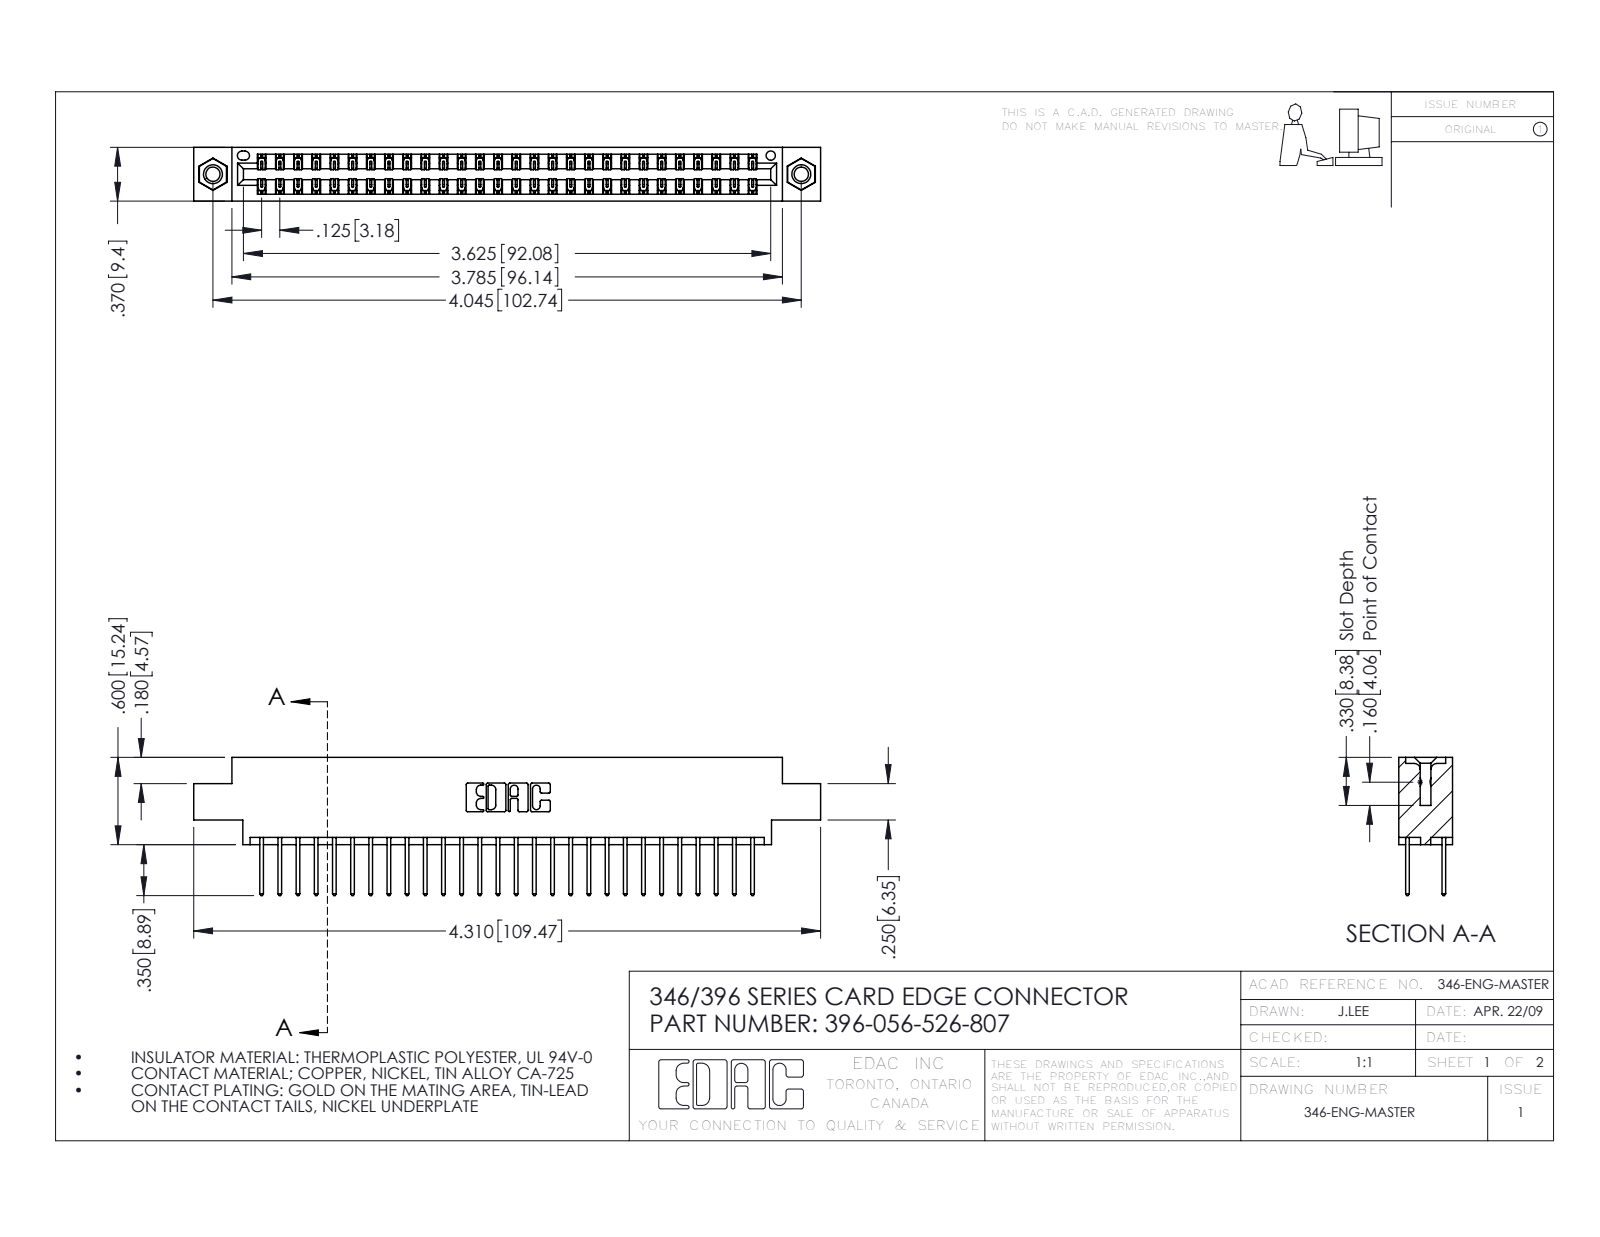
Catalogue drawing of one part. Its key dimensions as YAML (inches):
part_name: "346 Part_0.170 Offset - 0.156 Dia-TI; 345-250-001_345-250-005-103; 396-056-526-807; 345-292-001_345-293-126"
step_written_by: "SolidWorks 2016 (CONFIG_CONTROL_DESIGN)"
units: inches
bodies: {solids: 59, faces: 3098, planar: 2072, cylindrical: 1010, other: 16}
overall_size: [4.31, 0.95, 0.37]
volume: 0.64
surface_area: 22.98
round_holes:
  - {diameter: 0.098, count: 2}
  - {diameter: 0.125, count: 2}
  - {diameter: 0.156, count: 2}
  - {diameter: 0.064, count: 1}
round_bosses_or_shafts:
  - {diameter: 0.155, count: 2}
partial_cylinders:
  - {radius: 0.006, count: 84}
  - {radius: 0.01, count: 56}
  - {radius: 0.01, count: 22}
  - {radius: 0.007, count: 6}
  - {radius: 0.031, count: 6}
  - {radius: 0.026, count: 3}
  - {radius: 0.014, count: 2}
  - {radius: 0.022, count: 2}
face_to_face_distances: [0.048, 0.322, 0.25, 0.37, 0.072, 0.298, 0.025, 0.275, 0.222, 0.148]
hole_center_spacings: [0.246, 3.837, 4.045]
